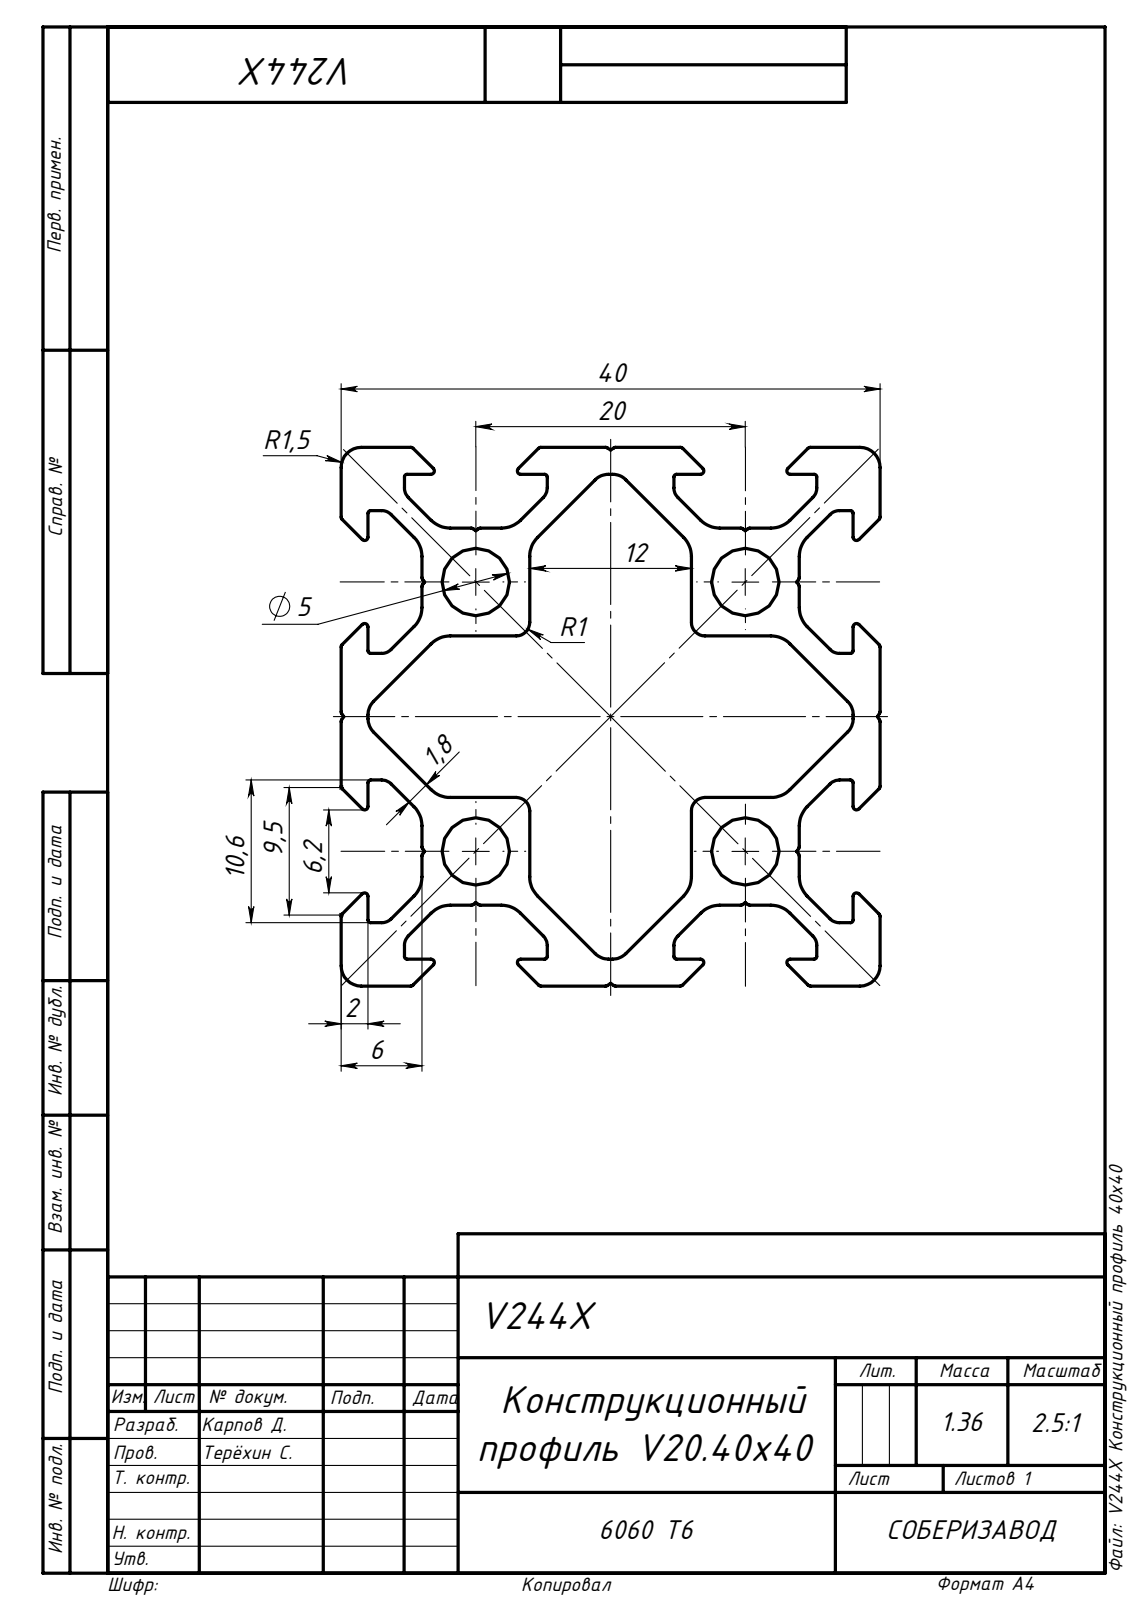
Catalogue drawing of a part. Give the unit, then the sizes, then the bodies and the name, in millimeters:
Units: millimetres
Overall size (bounding box): 1000 × 40 × 40
Round holes (diameter × count): ⌀5 ×4
Partial cylindrical surfaces — rounded edges, fillets, slot ends (radius × count): R0.25 ×56, R2 ×24, R1 ×20, R0.2 ×16, R1.4 ×8, R1.5 ×4
Main face-to-face distances: 14.14, 12, 14, 26, 2.83, 4.63, 16.97, 18.77, 40, 20
Hole centre spacings: 20, 28.28
Volume: 505 356 mm³ · Surface area: 461 130 mm²
Bodies: 1 solid, 286 faces (142 planar, 144 cylindrical, 0 other)
Part name (STEP PRODUCT): V244X Конструкционный профиль 40х40
STEP written by: SolidWorks 2019 (AUTOMOTIVE_DESIGN)
